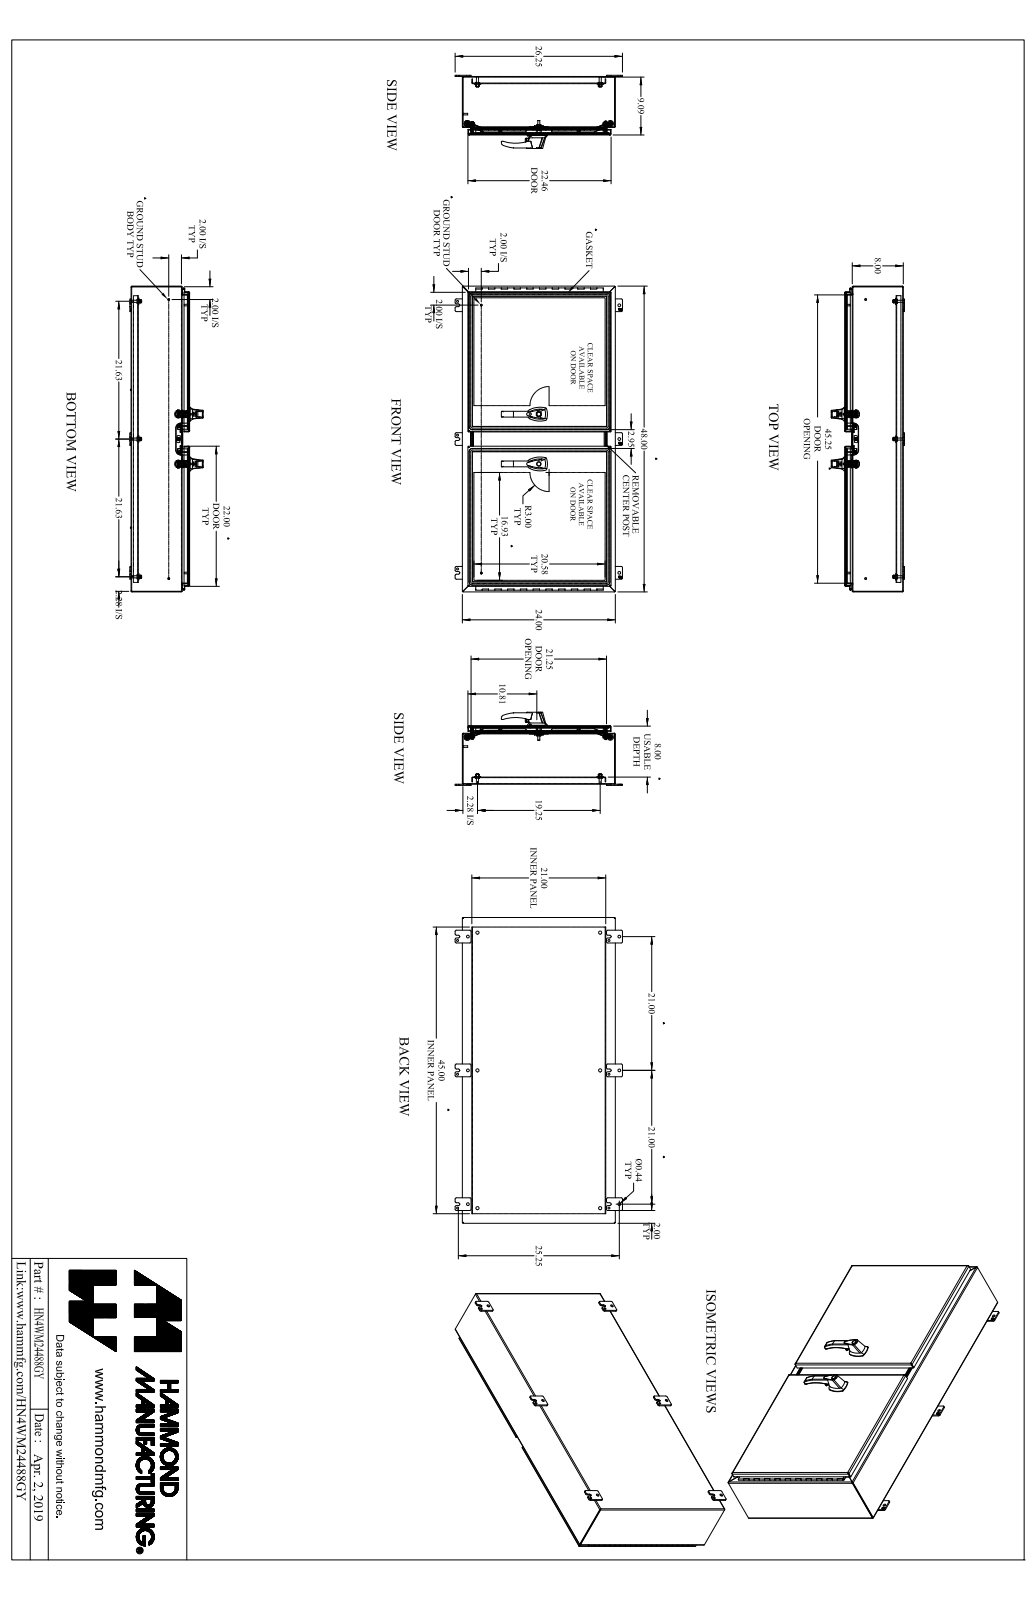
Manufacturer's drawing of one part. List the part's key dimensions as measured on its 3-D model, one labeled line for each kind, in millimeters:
Part name (STEP PRODUCT): HN4WM24488GY
STEP written by: SolidWorks 2018 (AUTOMOTIVE_DESIGN)
Units: millimetres
Bodies: 102 solids, 2636 faces (1243 planar, 1101 cylindrical, 292 other)
Overall size (bounding box): 1219.2 × 666.8 × 291.8
Volume: 8 782 000 mm³ · Surface area: 7 070 000 mm²
Round holes (diameter × count): ⌀6.4 ×10, ⌀8 ×9, ⌀7.7 ×8, ⌀5.1 ×6, ⌀7.8 ×6, ⌀12.7 ×6, ⌀6.5 ×4, ⌀7.1 ×4, ⌀7.1 ×4, ⌀8 ×4, ⌀9.9 ×4, ⌀10.5 ×4
Round bosses / shafts (diameter × count): ⌀25.4 ×10, ⌀7.1 ×8, ⌀16.5 ×6, ⌀9.5 ×6, ⌀8.4 ×6, ⌀7.4 ×6, ⌀19.1 ×4, ⌀16 ×4
Partial cylindrical surfaces — rounded edges, fillets, slot ends (radius × count): R3.2 ×37, R0.5 ×32, R4.8 ×27, R6.4 ×26, R1.5 ×22, R12.7 ×22, R1.2 ×19, R3.6 ×19
Main face-to-face distances: 2.4, 26.2, 2.4, 230.9, 228.5, 23.8, 233.3, 230.9, 28.6, 202.3
Hole centre spacings: 198.5, 152.4, 1181.9, 28.6, 32.7, 51.8, 184.8, 200.5
